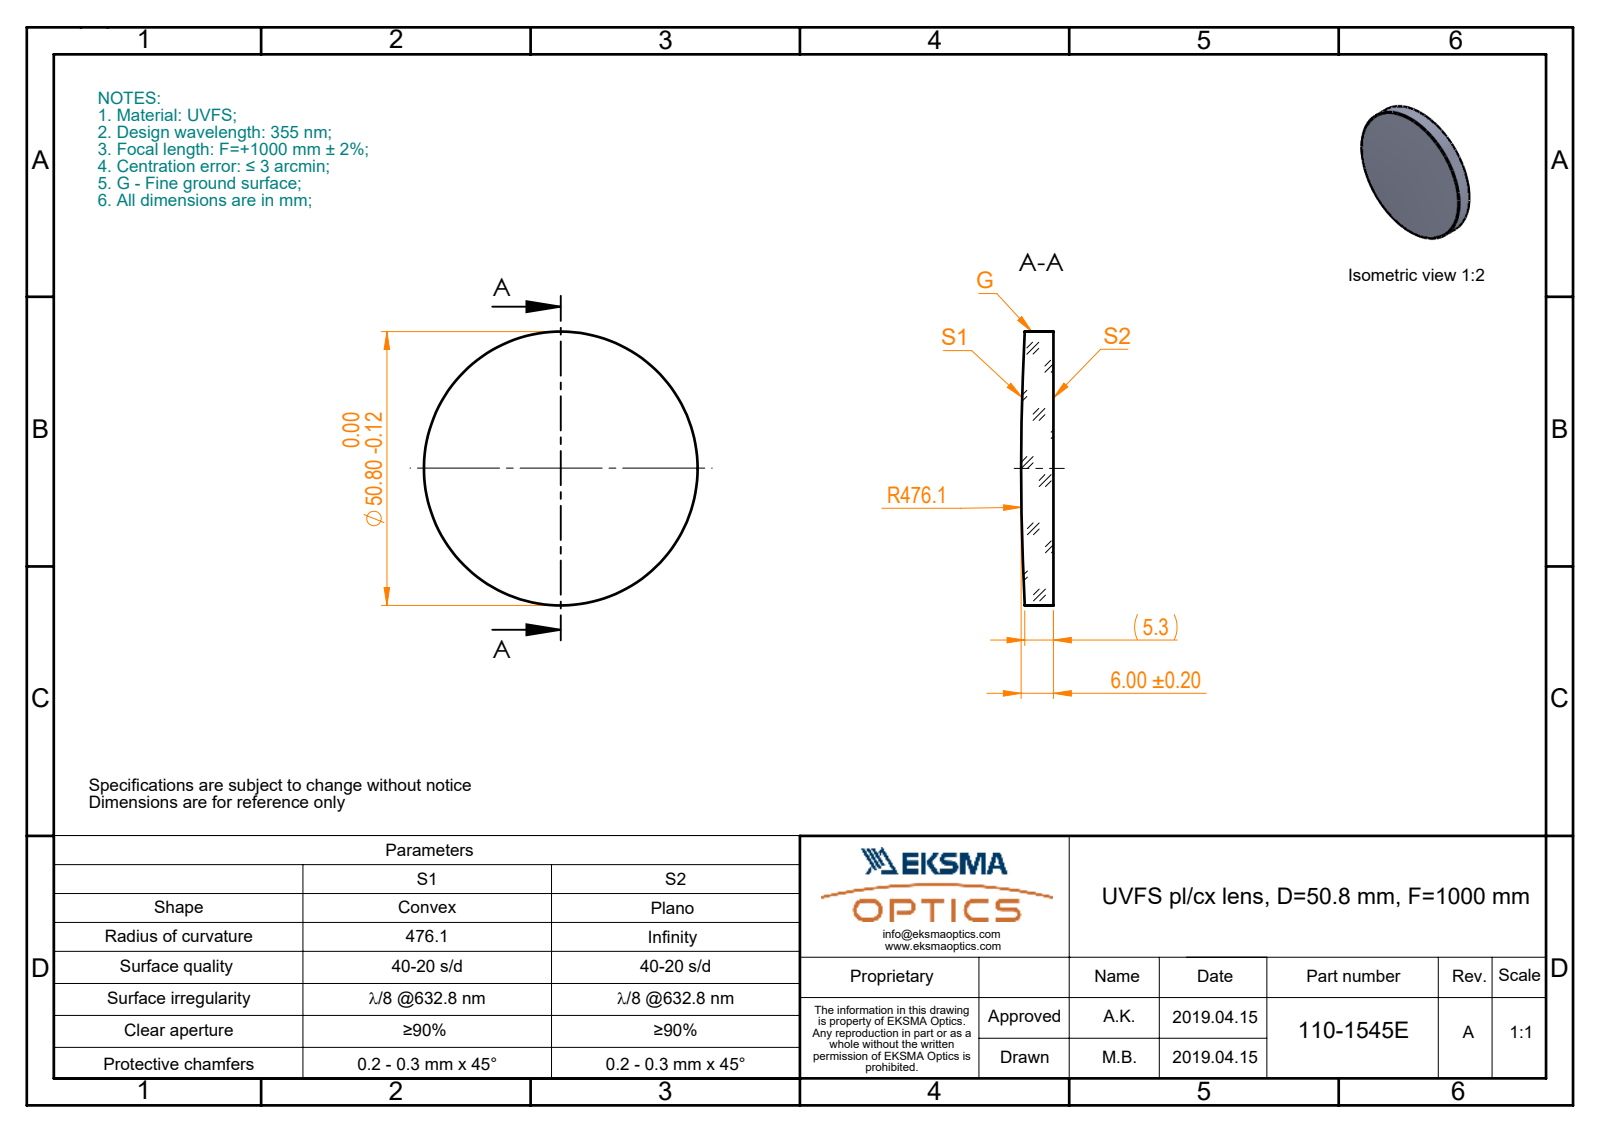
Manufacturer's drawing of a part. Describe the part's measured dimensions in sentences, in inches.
The part is named "110-1545E UVFS pl-cx 50.8 F1000". Its 3-D file was written by "SolidWorks 2017 (CONFIG_CONTROL_DESIGN)". It is 1 solid with 5 faces: 1 planar, 2 cylindrical and 2 other. Overall it measures 2 by 2 by 0.236 inches. Its volume is 0.7 cubic inches and its surface area 7.601 square inches. Round bosses or shafts: 1 of diameter 2.
